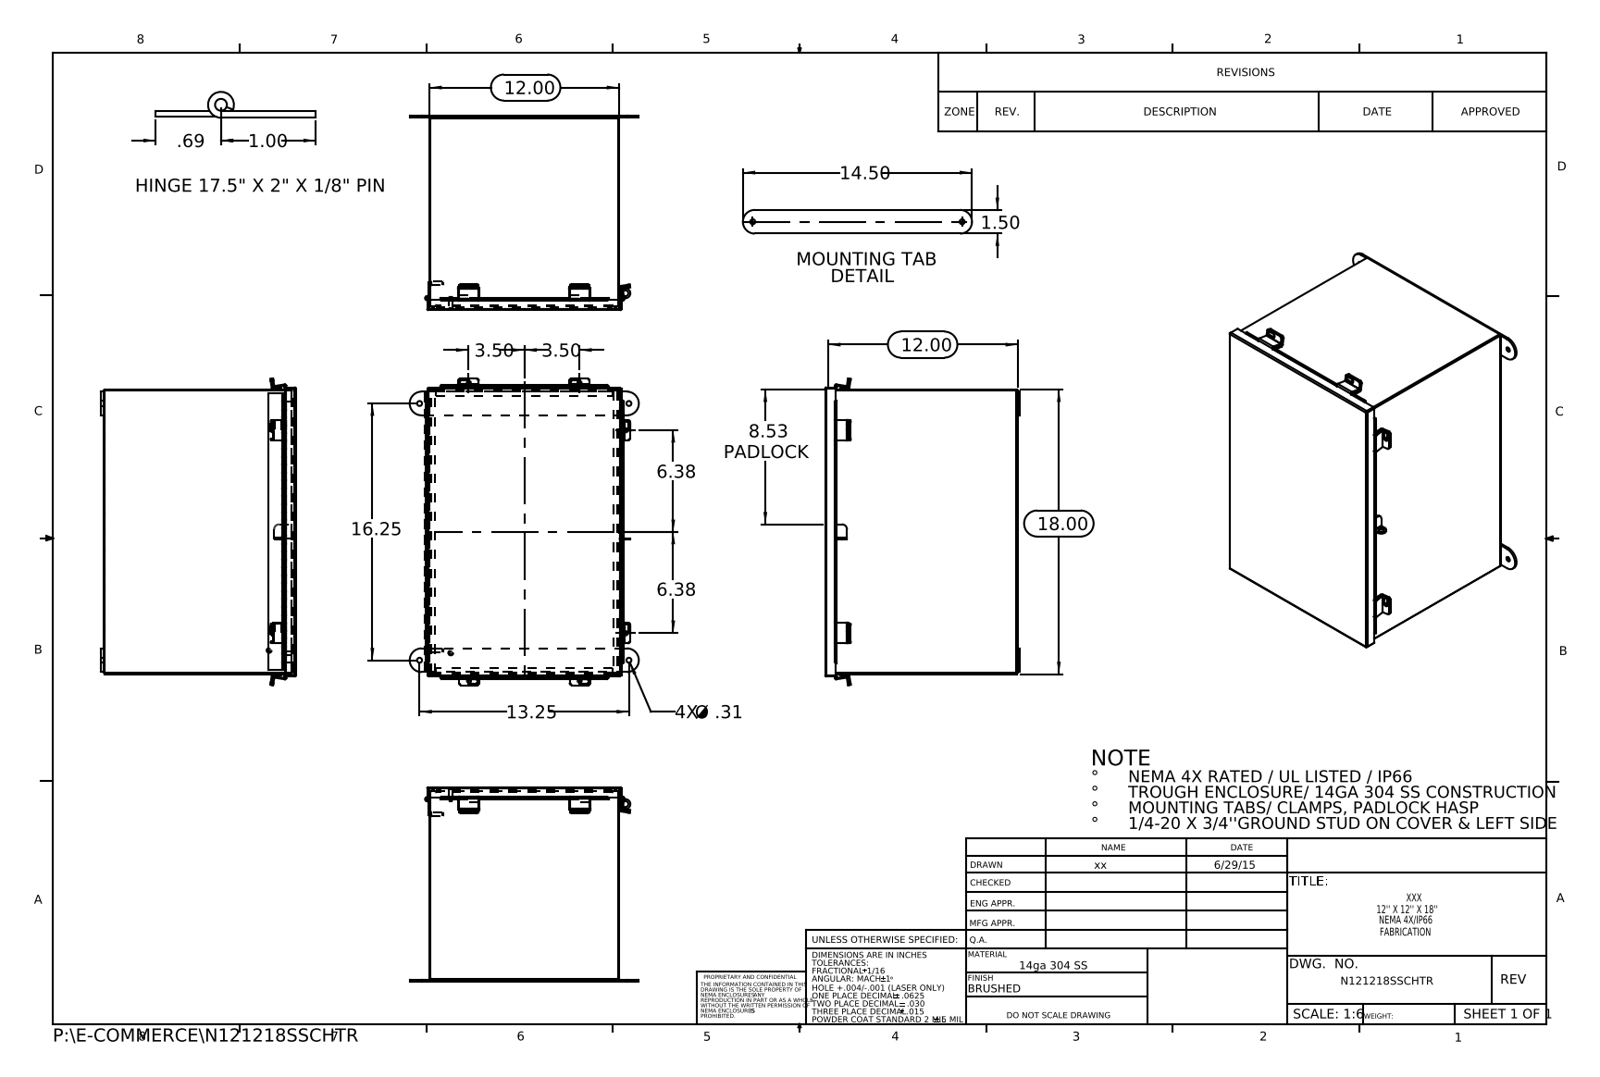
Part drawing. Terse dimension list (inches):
name: N121218SSCHTR HW-CD-S-25020-034; N121218SSCHTR Hinge Cover Side JIC; HW-CLH-JH-20154; N121218SSCHTR JIC Mounting Bracket (+8 more)
written by: SolidWorks 2015 (CONFIG_CONTROL_DESIGN)
unit: in
bodies: 23 solids, 824 faces (517 planar, 287 cylindrical, 20 other)
size: 19.407 × 14.5 × 12.337
volume: 99.91 in³; area: 2 650 in²
holes: 6× ⌀0.25, 4× ⌀0.313, 1× ⌀0.125, 1× ⌀0.375
bosses: 2× ⌀0.315, 2× ⌀0.236, 1× ⌀0.273, 1× ⌀0.25
rounds: 21× R0.125, 12× R0.009, 12× R0.133, 11× R0.013, 11× R0.088, 6× R0.083, 6× R0.1, 4× R0.75
face distances: 0.075, 11.925, 12.128, 17.925, 11.85, 12, 12.203, 12.053, 17.85, 18
hole spacings: 7, 13.25, 16.25, 20.968, 12.54, 12.85
